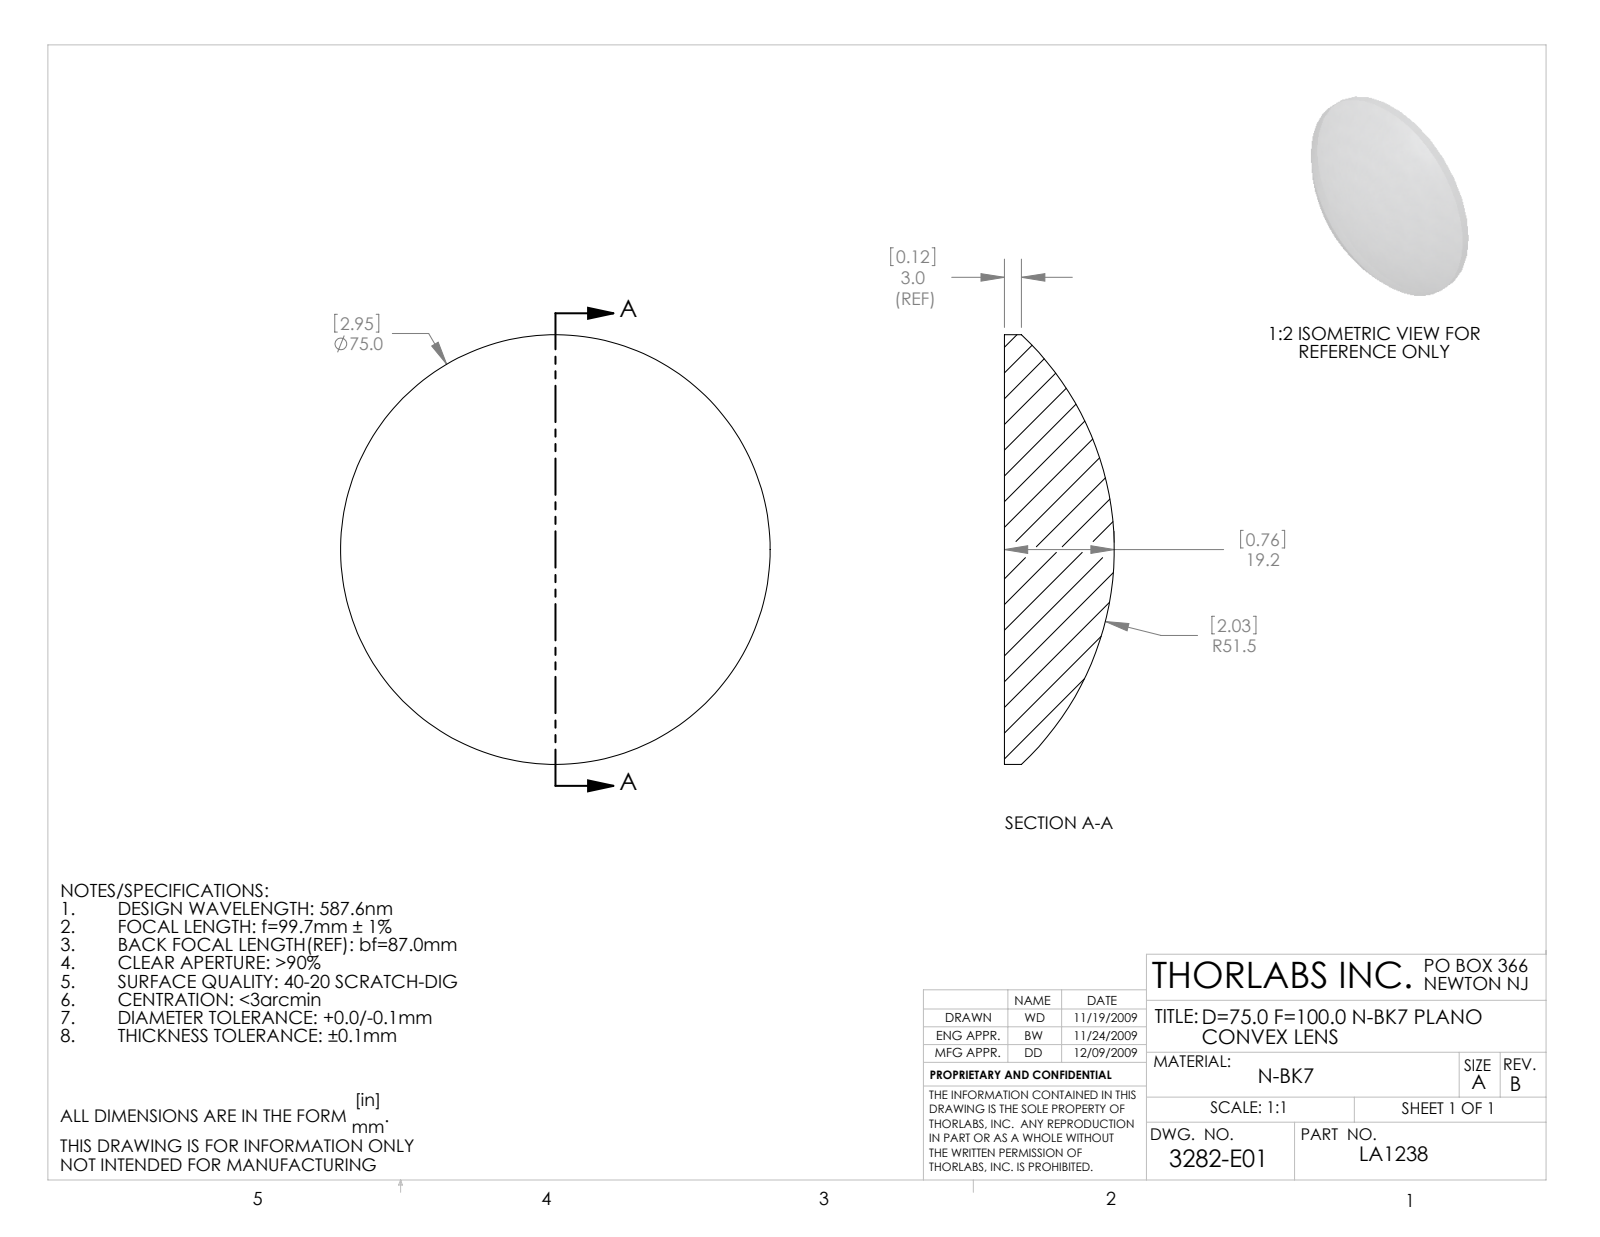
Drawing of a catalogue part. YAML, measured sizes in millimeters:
part_name: "3282-E0W"
step_written_by: "SolidWorks 2009 (AUTOMOTIVE_DESIGN)"
units: millimeters
bodies: {solids: 1, faces: 5, planar: 1, cylindrical: 2, other: 2}
overall_size: [75, 75, 19.19]
volume: 51218
surface_area: 10365
round_bosses_or_shafts:
  - {diameter: 75, count: 1}
